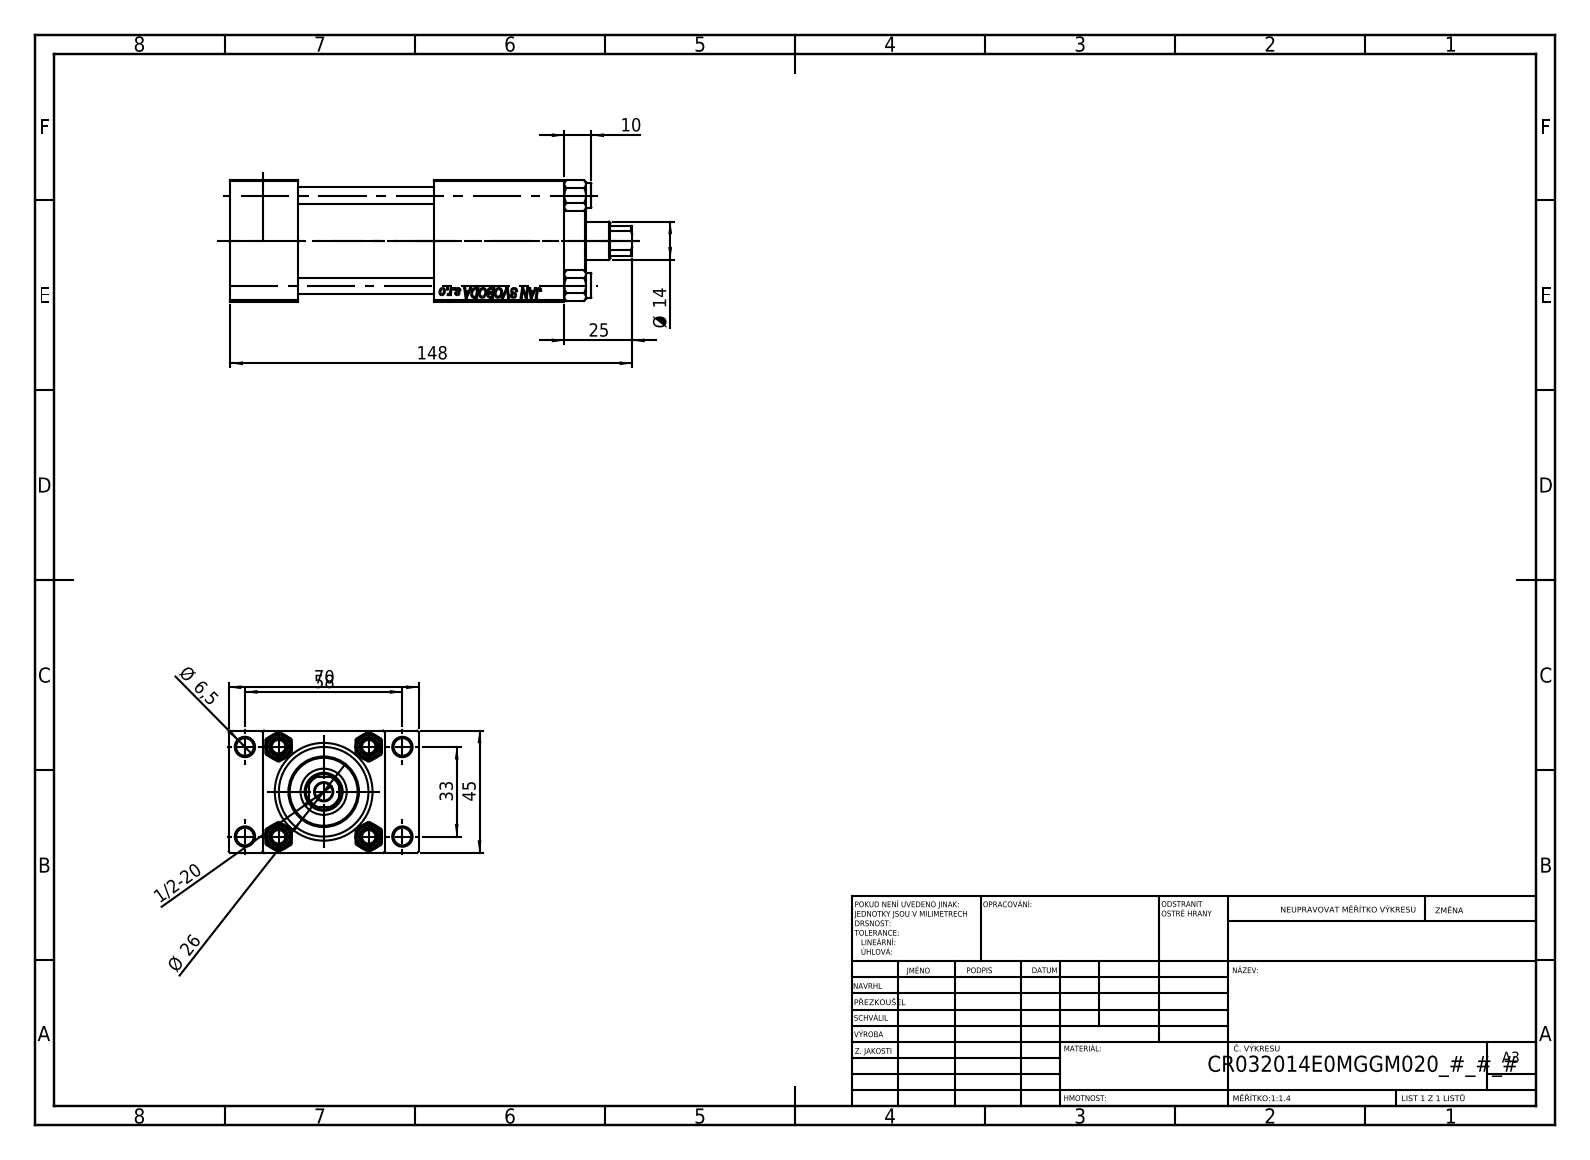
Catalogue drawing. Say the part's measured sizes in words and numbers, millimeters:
The part is named "V215CR_TYCINKA_E; NUT_M5_E; V215CR_VCP_E; V215CR_E_Body (+1 more)". Its 3-D file was written by "SolidWorks 2019 (CONFIG_CONTROL_DESIGN)". It is 11 solids with 1136 faces: 497 planar, 87 cylindrical and 552 other. Overall it measures 148 by 70 by 45 millimeters. Its volume is 220 073 cubic millimeters and its surface area 76 073 square millimeters. Round holes: 5 of diameter 6.5, 4 of diameter 6, 2 of diameter 7, 2 of diameter 13.16, 2 of diameter 20, 1 of diameter 14, 1 of diameter 17, 1 of diameter 24, 1 of diameter 32, 1 of diameter 33. Round bosses or shafts: 4 of diameter 9, 1 of diameter 38, 1 of diameter 26. Partial cylindrical surfaces (rounded edges, fillets, slot ends): 1 of radius 6.5. The main face-to-face distances are 45, 25, 12.5, 57.5, 123, 98, 70, 50, 75, 48. The hole center spacings are 12.4, 23.48, 33.2, 33.37, 35.35, 45.6, 56.35, 33.
